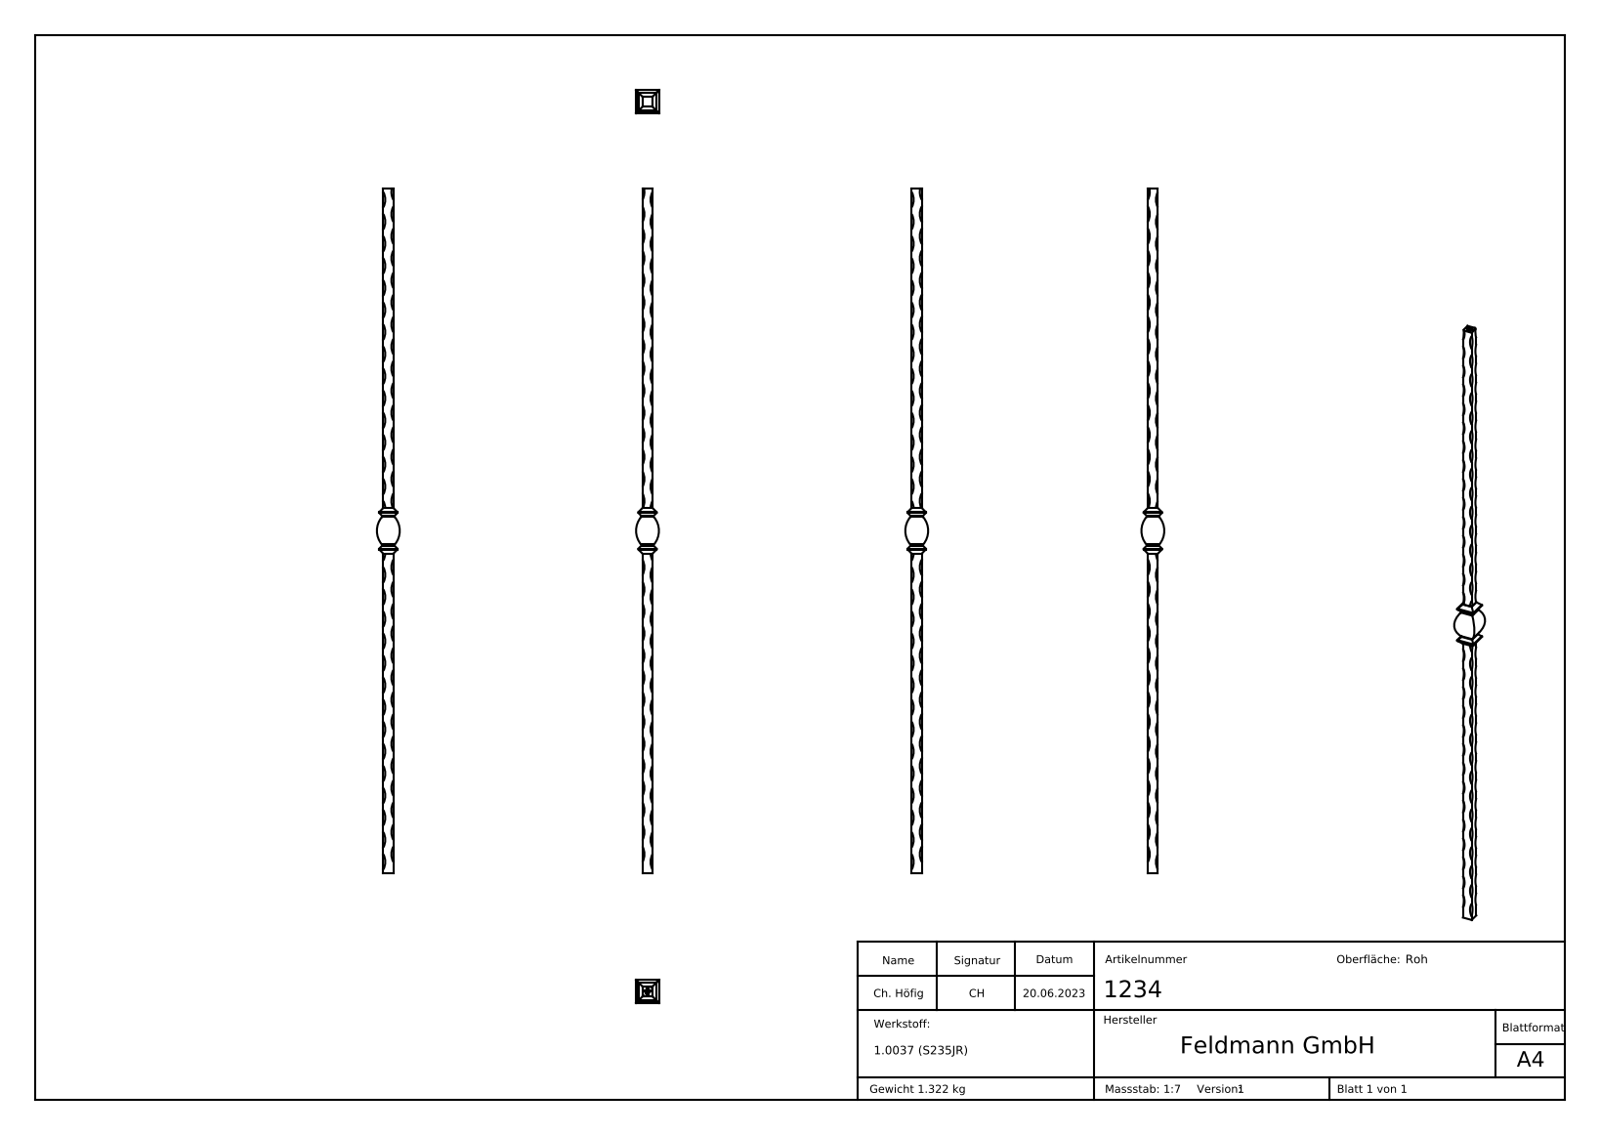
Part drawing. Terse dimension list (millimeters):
name: 1234
written by: SolidWorks 2018 (CONFIG_CONTROL_DESIGN)
unit: mm
bodies: 1 solid, 375 faces (149 planar, 20 cylindrical, 206 other)
size: 900 × 30 × 30
volume: 169 533 mm³; area: 49 030 mm²
rounds: 8× R0.8, 8× R1, 4× R28.17
face distances: 13, 17.8, 33.68, 51.48, 15.88, 900, 420, 480, 60, 899.9
